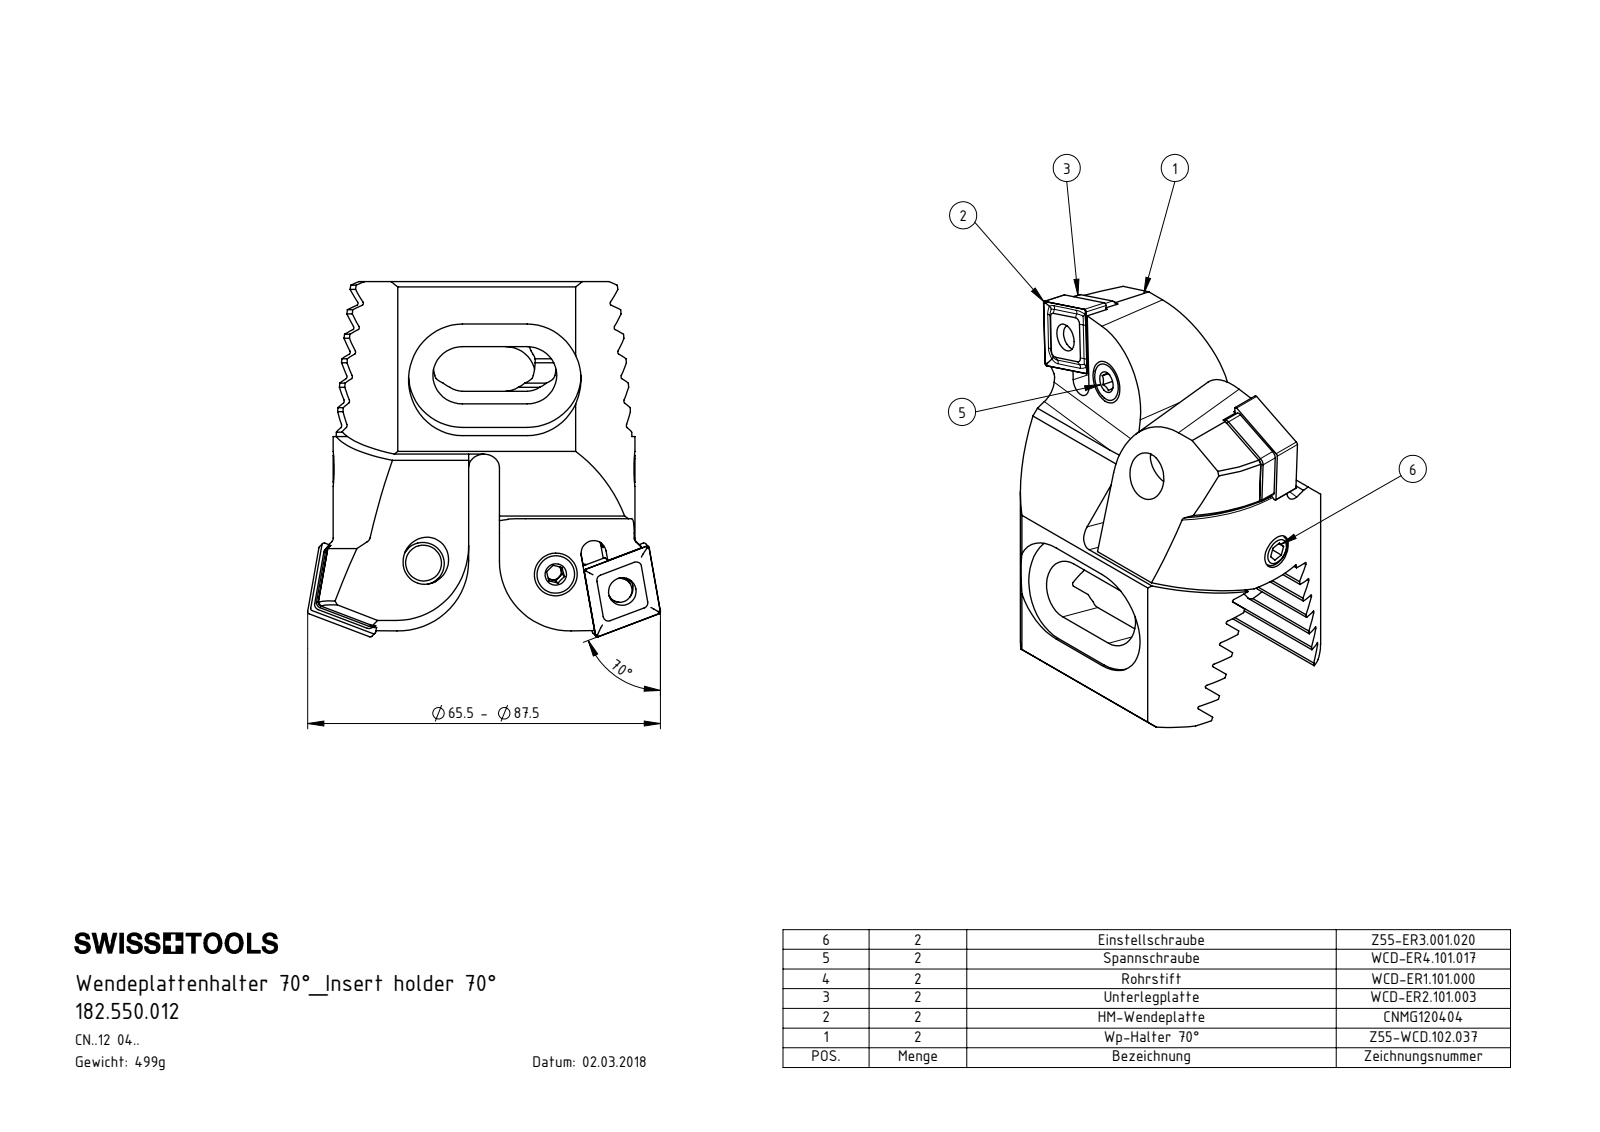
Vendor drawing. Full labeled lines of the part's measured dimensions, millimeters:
Part name (STEP PRODUCT): WCD-ER4.101.017_A; WCD; 182.550.012; CNMG120404 (+5 more)
STEP written by: SolidWorks 2017 (CONFIG_CONTROL_DESIGN)
Units: millimetres
Bodies: 14 solids, 578 faces (244 planar, 164 cylindrical, 170 other)
Overall size (bounding box): 65.92 × 65.5 × 44
Volume: 62 764 mm³ · Surface area: 26 357 mm²
Round holes (diameter × count): ⌀1 ×2, ⌀5.16 ×2, ⌀6.4 ×2, ⌀7 ×2, ⌀8.4 ×2, ⌀5 ×1
Round bosses / shafts (diameter × count): ⌀8 ×2, ⌀7.9 ×2, ⌀6.4 ×2, ⌀4.5 ×2, ⌀3.55 ×2, ⌀6 ×1, ⌀4 ×1
Partial cylindrical surfaces — rounded edges, fillets, slot ends (radius × count): R0.34 ×12, R1 ×10, R0.4 ×8, R2.5 ×6, R3 ×4, R5.5 ×4, R10 ×4, R2.1 ×2
Main face-to-face distances: 4.07, 8.14, 12.21, 16.28, 20.35, 1, 7.12, 44, 4.46, 28.75
Hole centre spacings: 12.8, 15, 12.85, 12.86, 28.98
